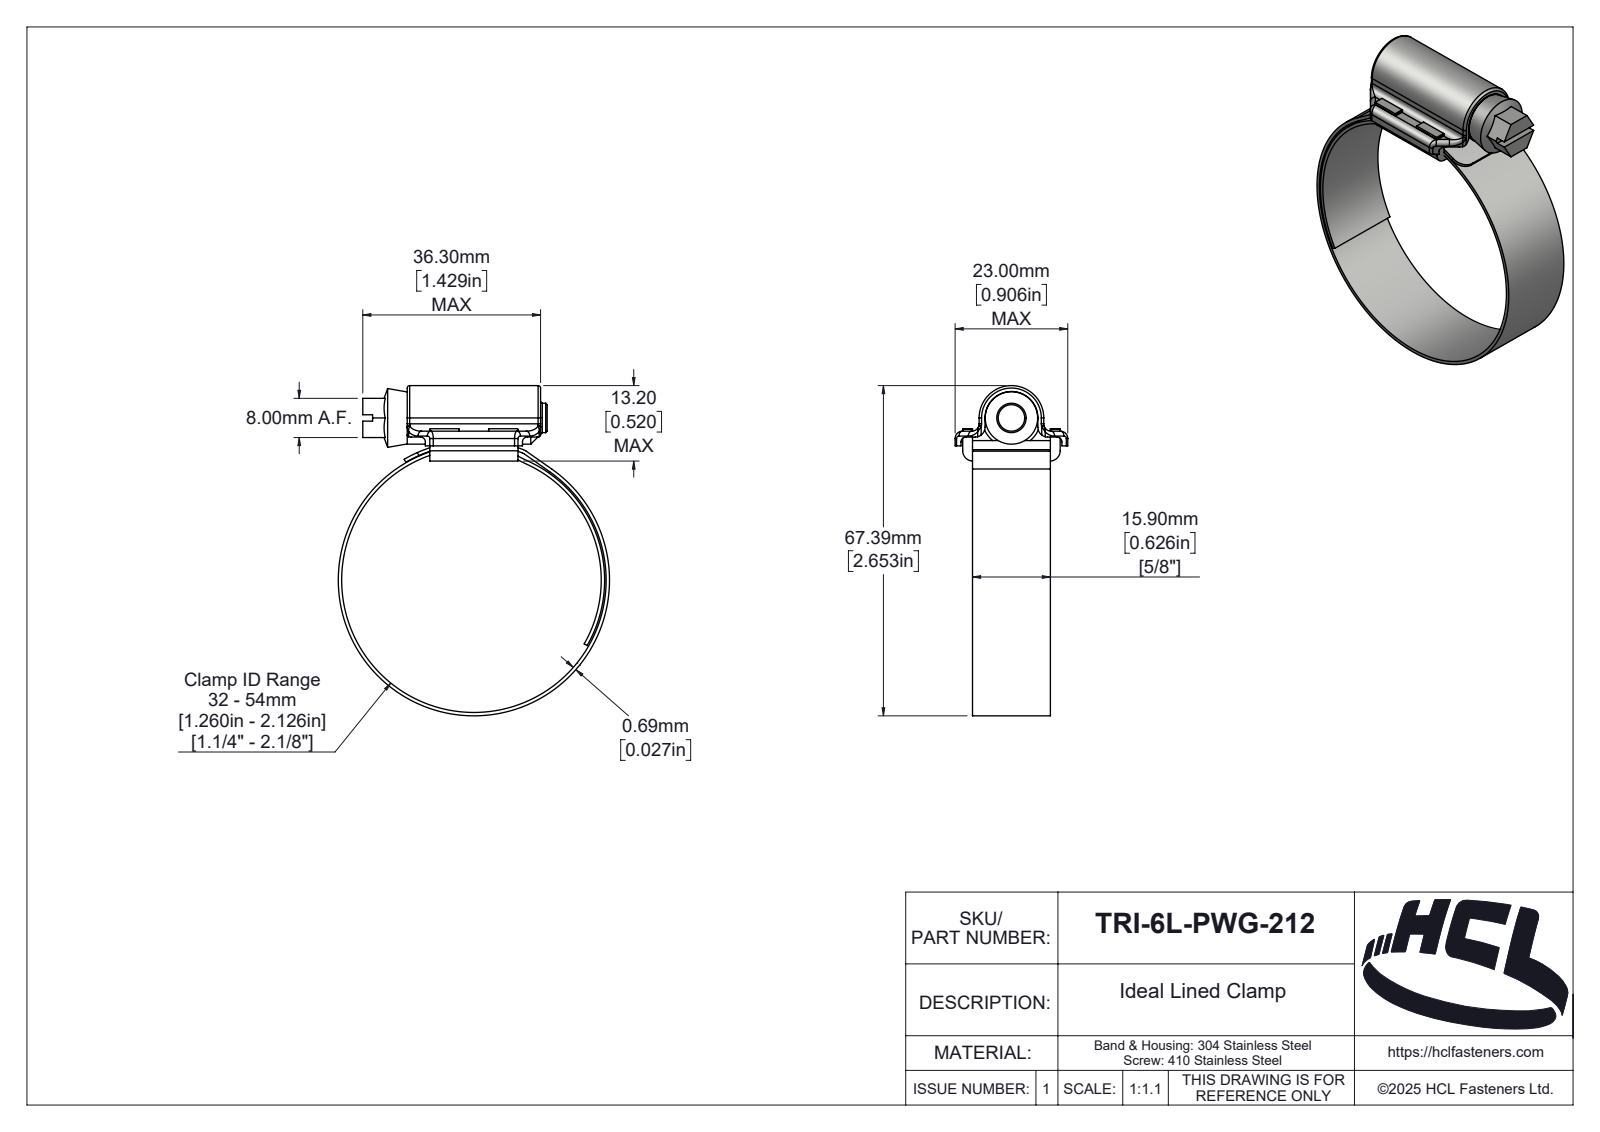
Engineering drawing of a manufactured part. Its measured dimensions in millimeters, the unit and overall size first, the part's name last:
Units: millimetres
Overall size (bounding box): 67.39 × 55.38 × 23
Round holes (diameter × count): ⌀54 ×1
Round bosses / shafts (diameter × count): ⌀55.38 ×1, ⌀10.7 ×1, ⌀6 ×1
Partial cylindrical surfaces — rounded edges, fillets, slot ends (radius × count): R1 ×14, R0.5 ×4, R1.5 ×4, R2 ×3, R0.1 ×2, R2.1 ×2, R3 ×2, R0.46 ×1
Main face-to-face distances: 2, 15.9, 17.9, 4.9, 1.2, 4.55, 3.35, 15.35, 2.55, 13.35
Volume: 7 852 mm³ · Surface area: 12 645 mm²
Bodies: 4 solids, 268 faces (87 planar, 102 cylindrical, 79 other)
Part name (STEP PRODUCT): TRI-6L-PWG-212
STEP written by: SolidWorks 2025 (AUTOMOTIVE_DESIGN)
